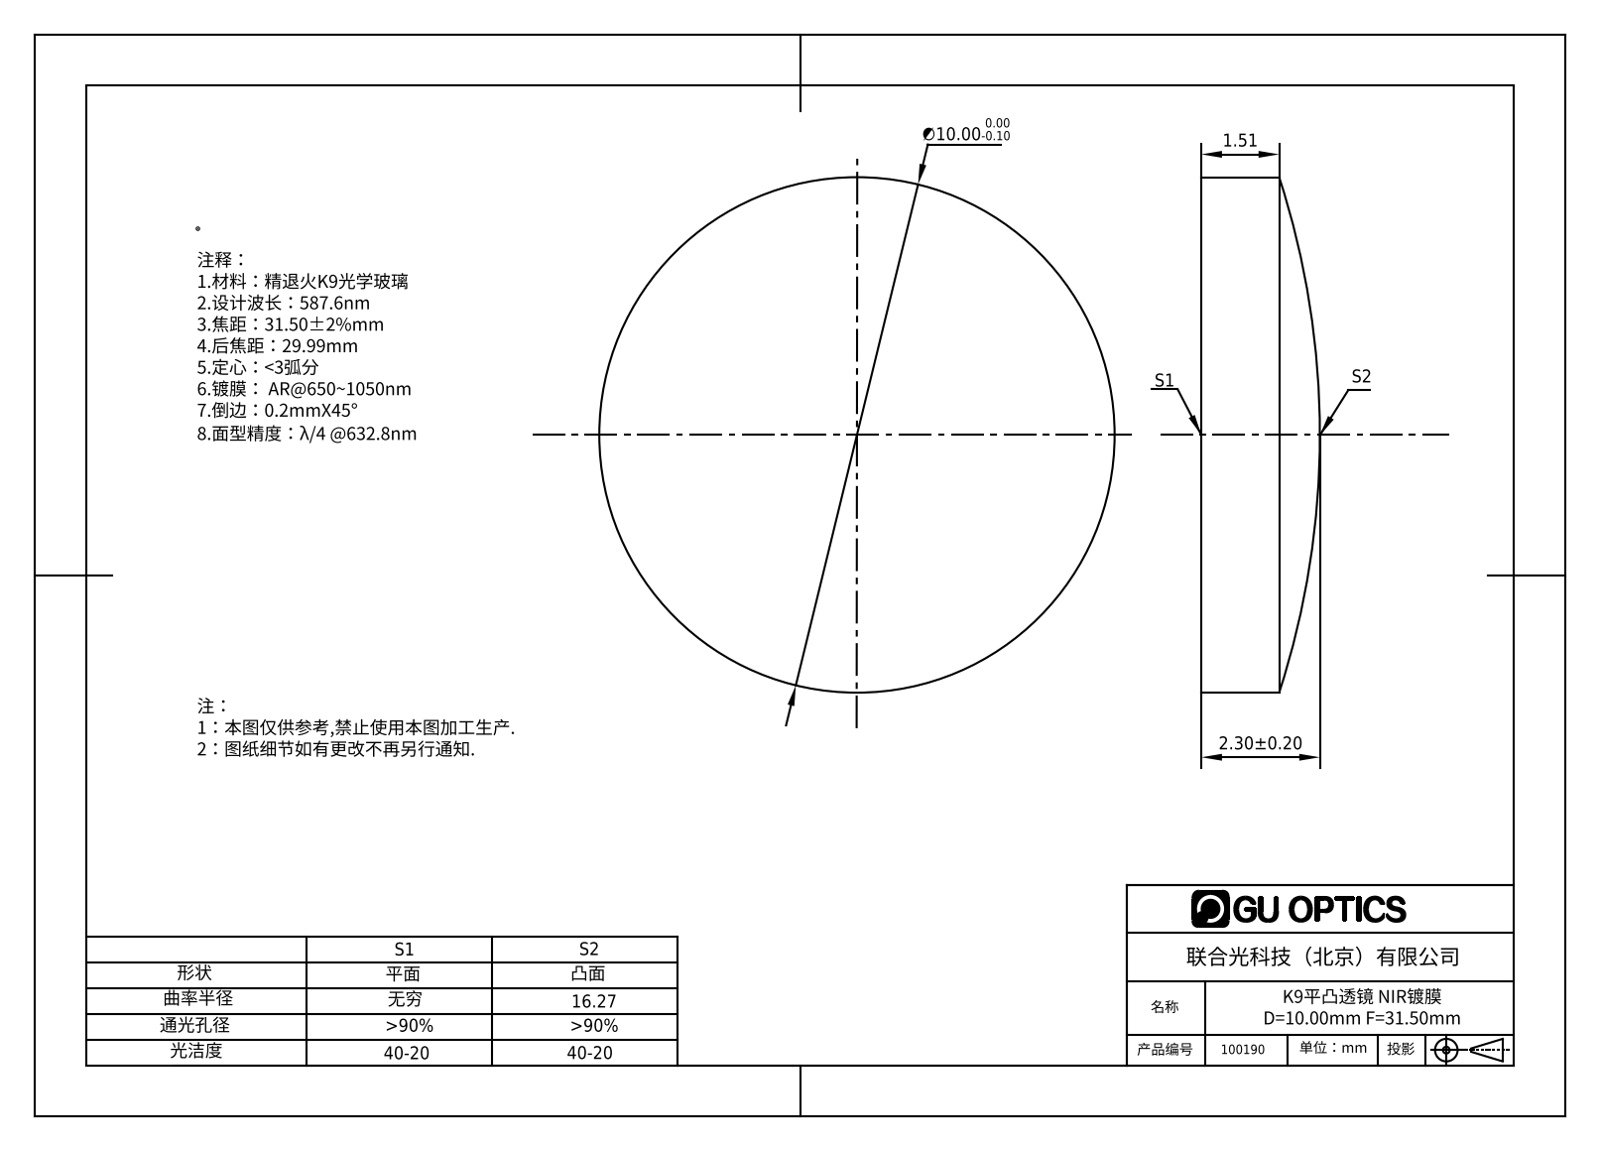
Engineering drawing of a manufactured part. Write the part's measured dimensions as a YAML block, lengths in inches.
part_name: "100190"
step_written_by: "SolidWorks 2016 (AUTOMOTIVE_DESIGN)"
units: inches
bodies: {solids: 1, faces: 5, planar: 1, cylindrical: 2, other: 2}
overall_size: [0.394, 0.394, 0.091]
volume: 0.009
surface_area: 0.319
round_bosses_or_shafts:
  - {diameter: 0.394, count: 1}
